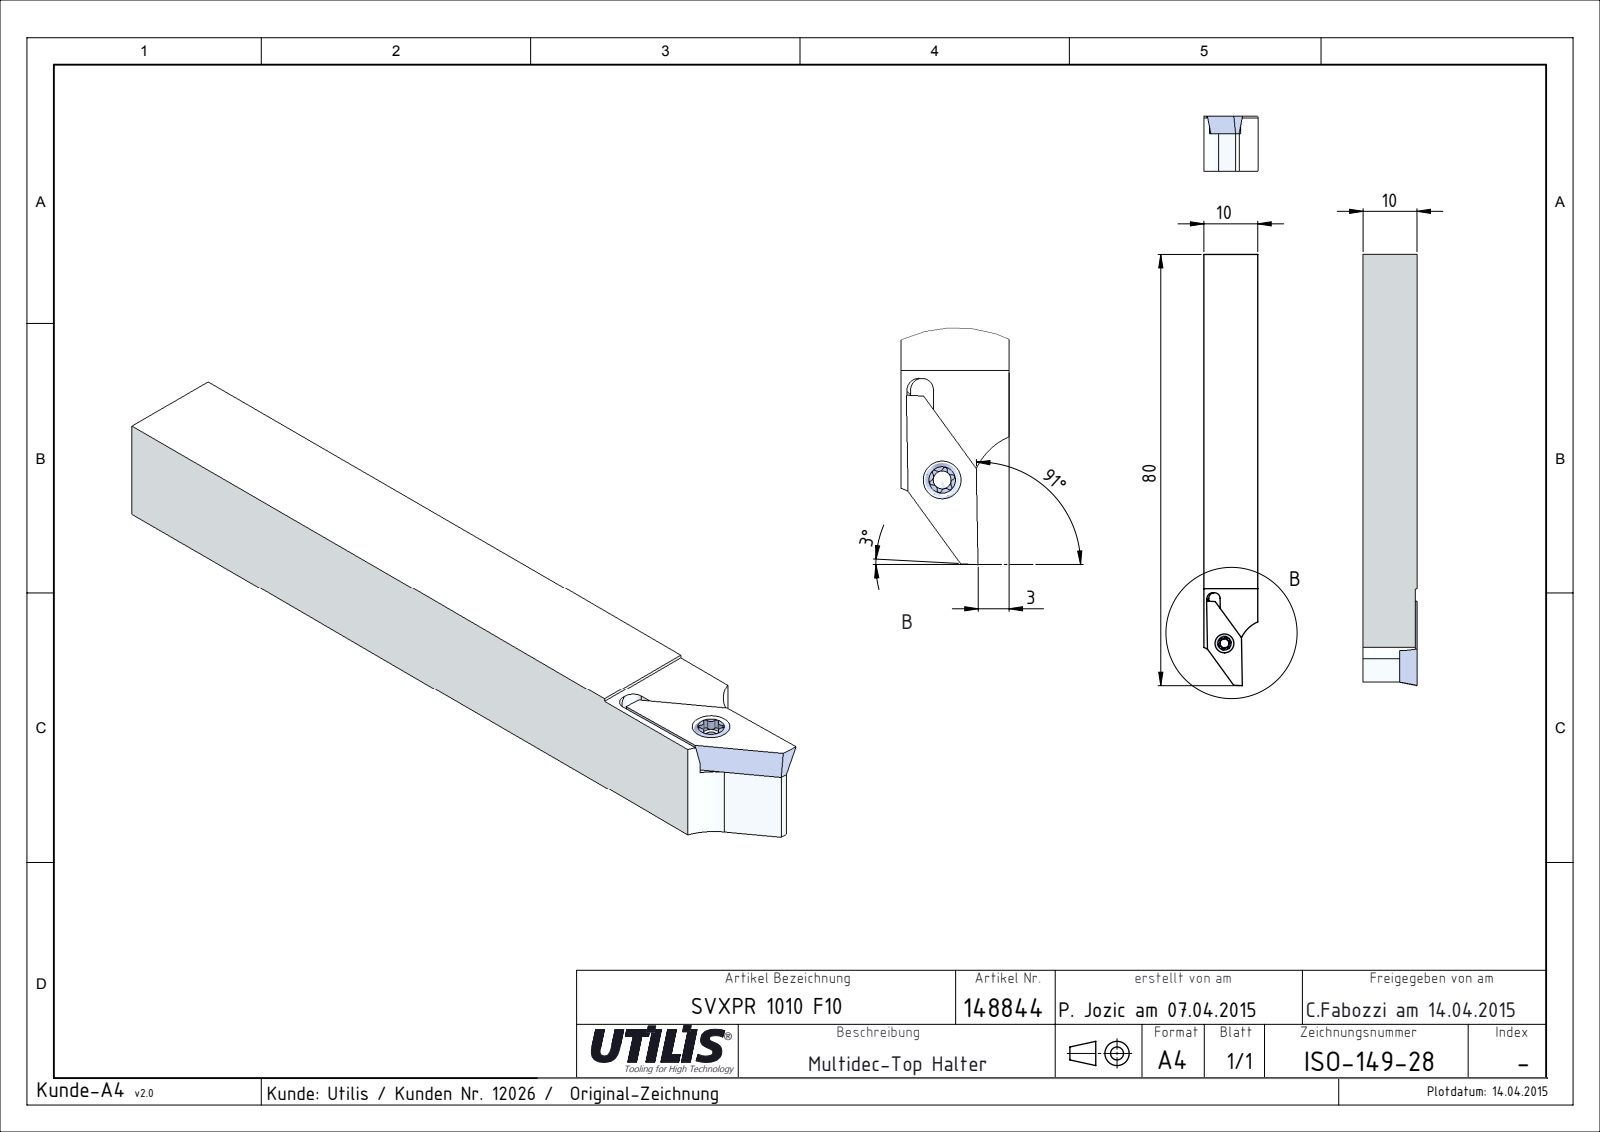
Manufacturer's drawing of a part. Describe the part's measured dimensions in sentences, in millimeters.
The part is named "ISO-149-Kunde_28; VPGT 10 R_VPGT 10 R; ISO-149-28; MSP-7_M2,5X6-TX8 CERATIZIT Schraube". Its 3-D file was written by "SolidWorks 2015 (CONFIG_CONTROL_DESIGN)". It is 3 solids with 71 faces: 27 planar, 27 cylindrical and 17 other. Overall it measures 80 by 10 by 10 millimeters. Its volume is 7 334 cubic millimeters and its surface area 3 554 square millimeters. Round holes: 1 of diameter 2.05, 1 of diameter 3. Round bosses or shafts: 1 of diameter 3.45, 1 of diameter 2.5. Partial cylindrical surfaces (rounded edges, fillets, slot ends): 6 of radius 0.2, 6 of radius 0.45, 2 of radius 6, 1 of radius 1.05. The main face-to-face distances are 10, 6.82, 3.18, 9.7, 2.88, 5.33, 2.1, 3.23, 5.32, 62.
